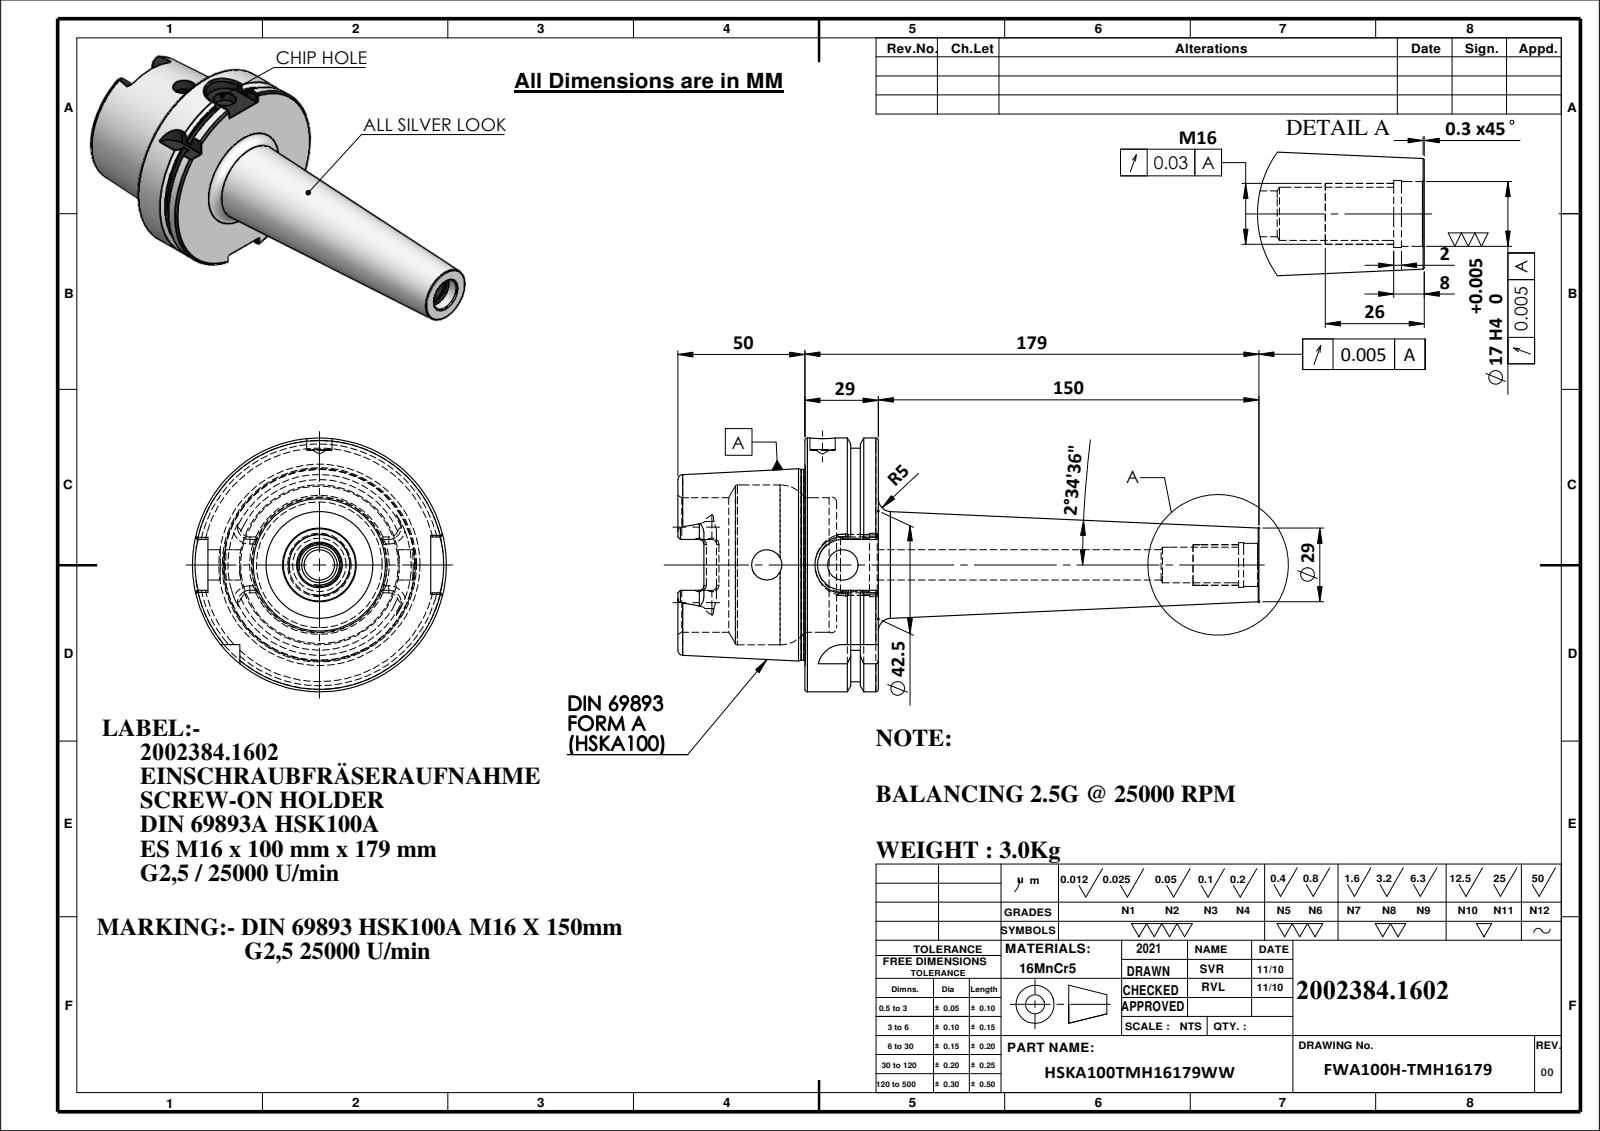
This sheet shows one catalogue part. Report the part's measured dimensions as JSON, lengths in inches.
{"part_name": "9100A-ES8M16150", "step_written_by": "SolidWorks 2018 (CONFIG_CONTROL_DESIGN)", "units": "inches", "bodies": {"solids": 1, "faces": 174, "planar": 50, "cylindrical": 52, "other": 72}, "overall_size": [9.014, 3.937, 3.937], "volume_in3": 23.65, "surface_area_in2": 110.8, "round_holes": [[0.472, 3], [0.394, 1], [0.551, 1], [0.669, 1], [0.693, 1], [0.827, 1], [0.984, 1], [2.087, 1], [2.48, 1]], "round_bosses_or_shafts": [[3.937, 1], [3.622, 1], [2.959, 1]], "partial_cylinders_radius": [[0.071, 6], [0.192, 4], [0.394, 2], [0.433, 1]], "face_to_face_distances": [1.14, 0.492, 0.648, 1.969, 2.461, 3.108, 2.83, 0.861, 0.369, 0.279], "hole_center_spacings": [1.181]}
